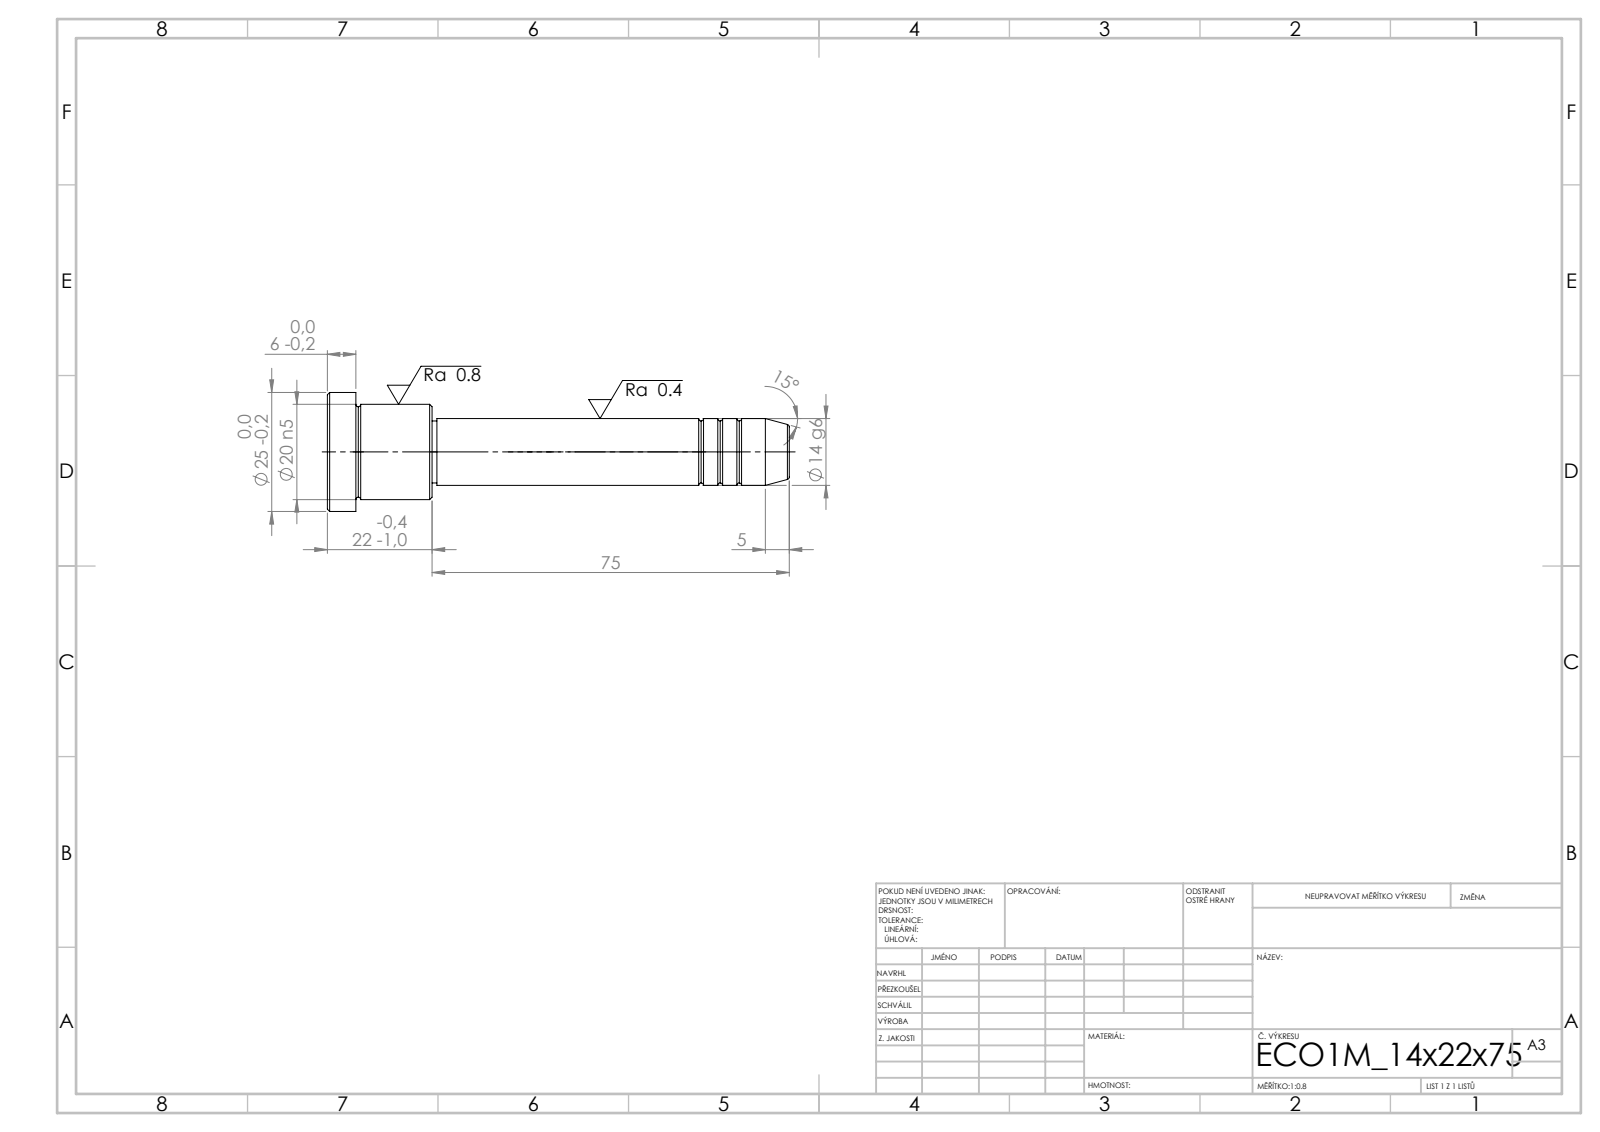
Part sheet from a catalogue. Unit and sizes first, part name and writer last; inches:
Units: inches
Overall size (bounding box): 3.819 × 0.984 × 0.984
Round bosses / shafts (diameter × count): ⌀0.984 ×1, ⌀0.787 ×1, ⌀0.551 ×1, ⌀0.512 ×1
Main face-to-face distances: 0.236, 0.63, 0.866, 2.953, 3.583, 3.819, 2.913, 0.039, 0.669, 0.906
Volume: 1.176 in³ · Surface area: 8.961 in²
Bodies: 1 solid, 43 faces (5 planar, 14 cylindrical, 24 other)
STEP written by: SolidWorks 2019 (CONFIG_CONTROL_DESIGN)
